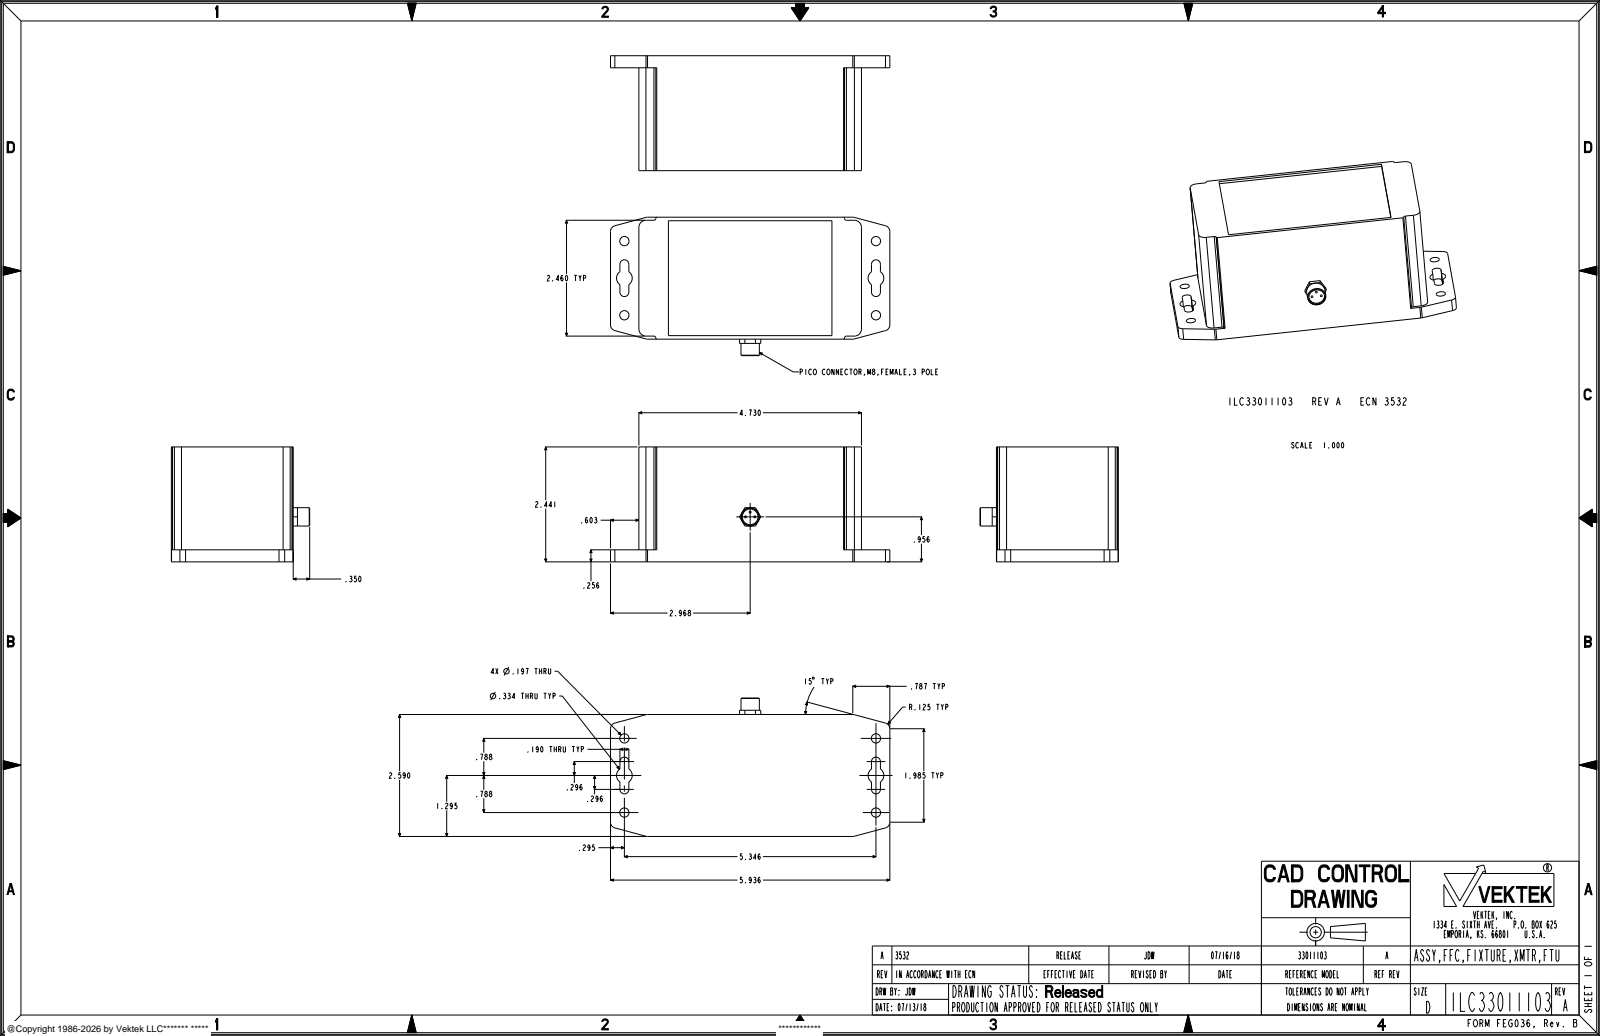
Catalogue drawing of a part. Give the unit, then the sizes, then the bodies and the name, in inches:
Units: inches
Overall size (bounding box): 5.936 × 2.94 × 2.441
Round holes (diameter × count): ⌀0.197 ×4, ⌀0.04 ×3, ⌀0.335 ×1
Round bosses / shafts (diameter × count): ⌀0.39 ×1
Partial cylindrical surfaces — rounded edges, fillets, slot ends (radius × count): R0.125 ×8, R0.02 ×4, R0.04 ×4, R0.095 ×4, R0.15 ×4, R0.167 ×2
Main face-to-face distances: 2.59, 2.391, 4.73, 2.441, 0.05, 0.256, 2.135, 2.185, 0.065, 2.525
Hole centre spacings: 0.1, 0.141, 1.575, 5.346, 5.573, 0.2
Volume: 29.87 in³ · Surface area: 67.22 in²
Bodies: 1 solid, 100 faces (52 planar, 46 cylindrical, 2 other)
Part name (STEP PRODUCT): ILC33011103
STEP written by: PRO/ENGINEER BY PARAMETRIC TECHNOLOGY CORPORATION, 2013320 (AUTOMOTIVE_DESIGN)
